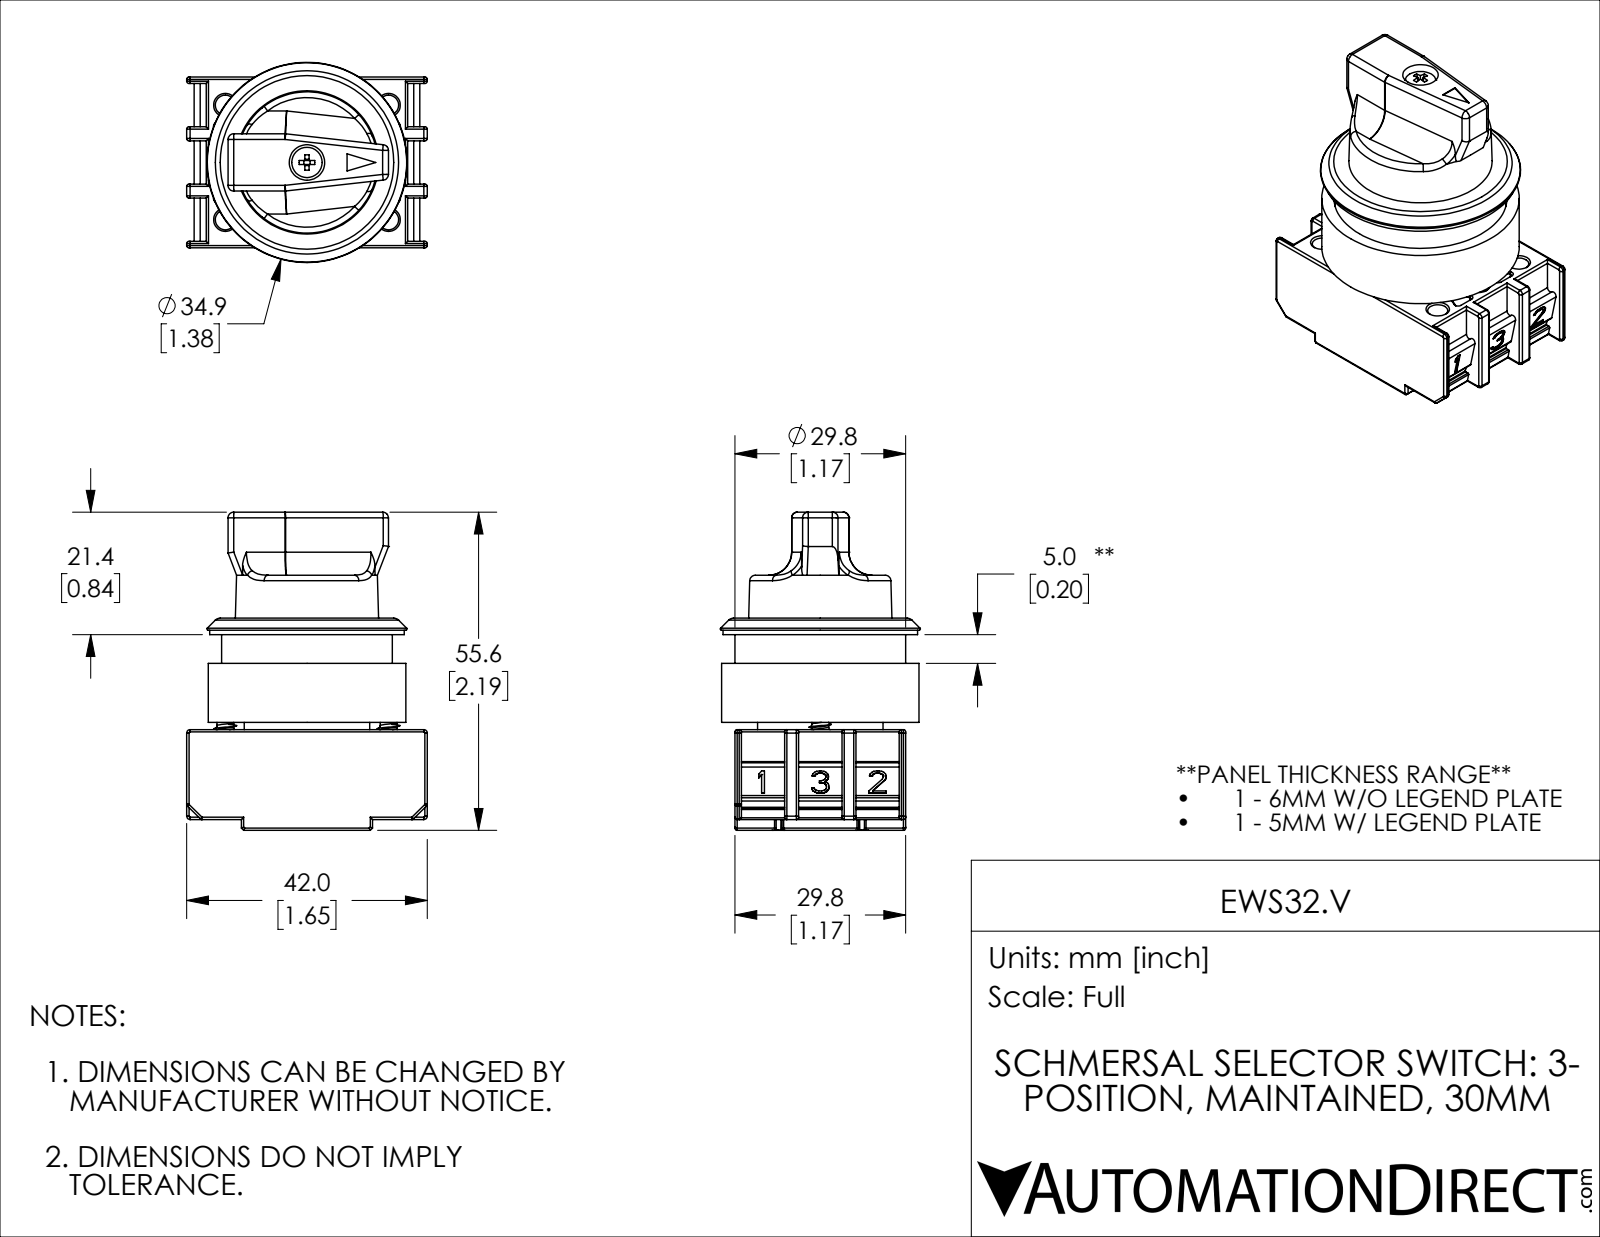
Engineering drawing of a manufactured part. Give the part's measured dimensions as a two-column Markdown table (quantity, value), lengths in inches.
| quantity | value |
| --- | --- |
| part name | EWS32.V |
| STEP written by | SolidWorks 2019 (CONFIG_CONTROL_DESIGN) |
| units | inches |
| bodies | 5 solids, 1701 faces (641 planar, 592 cylindrical, 468 other) |
| overall size | 2.187 × 1.654 × 1.375 |
| volume | 1.759 in³ |
| surface area | 40.12 in² |
| round holes (diameter × count) | 0.138 × 6, 0.203 × 6, 0.079 × 4, 0.197 × 4, 0.065 × 2, 0.077 × 2, 0.244 × 1, 0.36 × 1, 0.433 × 1, 0.551 × 1, 0.748 × 1, 0.866 × 1 |
| round bosses / shafts (diameter × count) | 0.189 × 4, 0.115 × 2, 1.358 × 1, 1.339 × 1, 1.173 × 1, 1.004 × 1, 0.862 × 1, 0.728 × 1 |
| partial cylindrical surfaces (radius × count) | 0.016 × 120, 0.012 × 48, 0.039 × 30, 0.008 × 28, 0.02 × 14, 0.024 × 8, 0.031 × 6, 0.157 × 4 |
| main face-to-face distances | 0.634, 0.683, 0.742, 1.173, 0.717, 0.083, 0.72, 0.886, 1.459, 0.555 |
| hole center spacings | 0.564, 0.119, 0.167, 0.236, 0.246, 0.278, 0.355, 0.394 |
